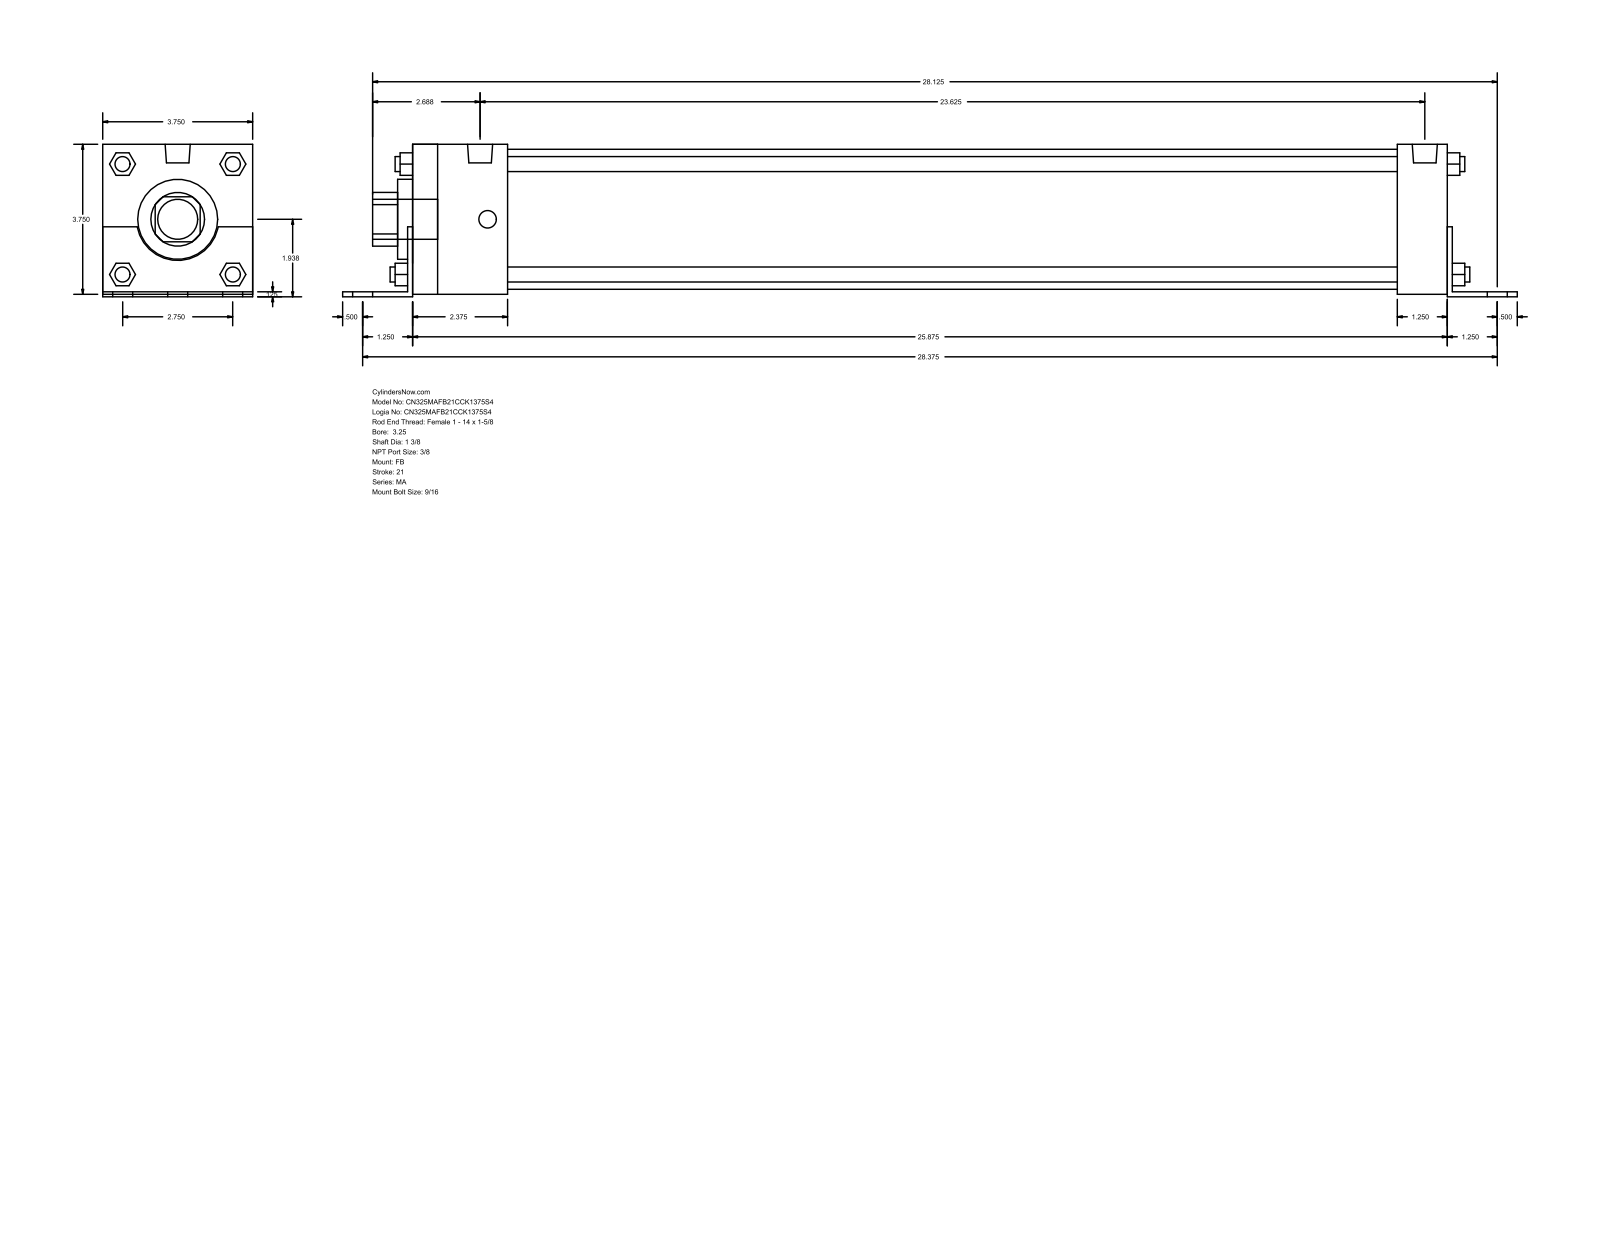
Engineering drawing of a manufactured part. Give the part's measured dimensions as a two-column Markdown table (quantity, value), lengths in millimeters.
| quantity | value |
| --- | --- |
| part name | MA_FB__0325_1.375 |
| STEP written by | GSSL Pune (CONFIG_CONTROL_DESIGN) |
| units | millimeters |
| bodies | 0 solids, 140 faces (105 planar, 35 cylindrical, 0 other) |
| overall size | 746.12 × 96.84 × 95.25 |
| round holes (diameter × count) | 34.92 × 1, 50.8 × 1, 88.9 × 1 |
| round bosses / shafts (diameter × count) | 14.29 × 6, 11.11 × 4, 9.53 × 4, 15.93 × 2, 25.4 × 1 |
| partial cylindrical surfaces (radius × count) | 17.06 × 1, 26.16 × 1 |
| main face-to-face distances | 95.24, 3.17, 1.59, 96.83, 1.58, 93.66, 3.18, 657.22, 660.4, 60.32 |
